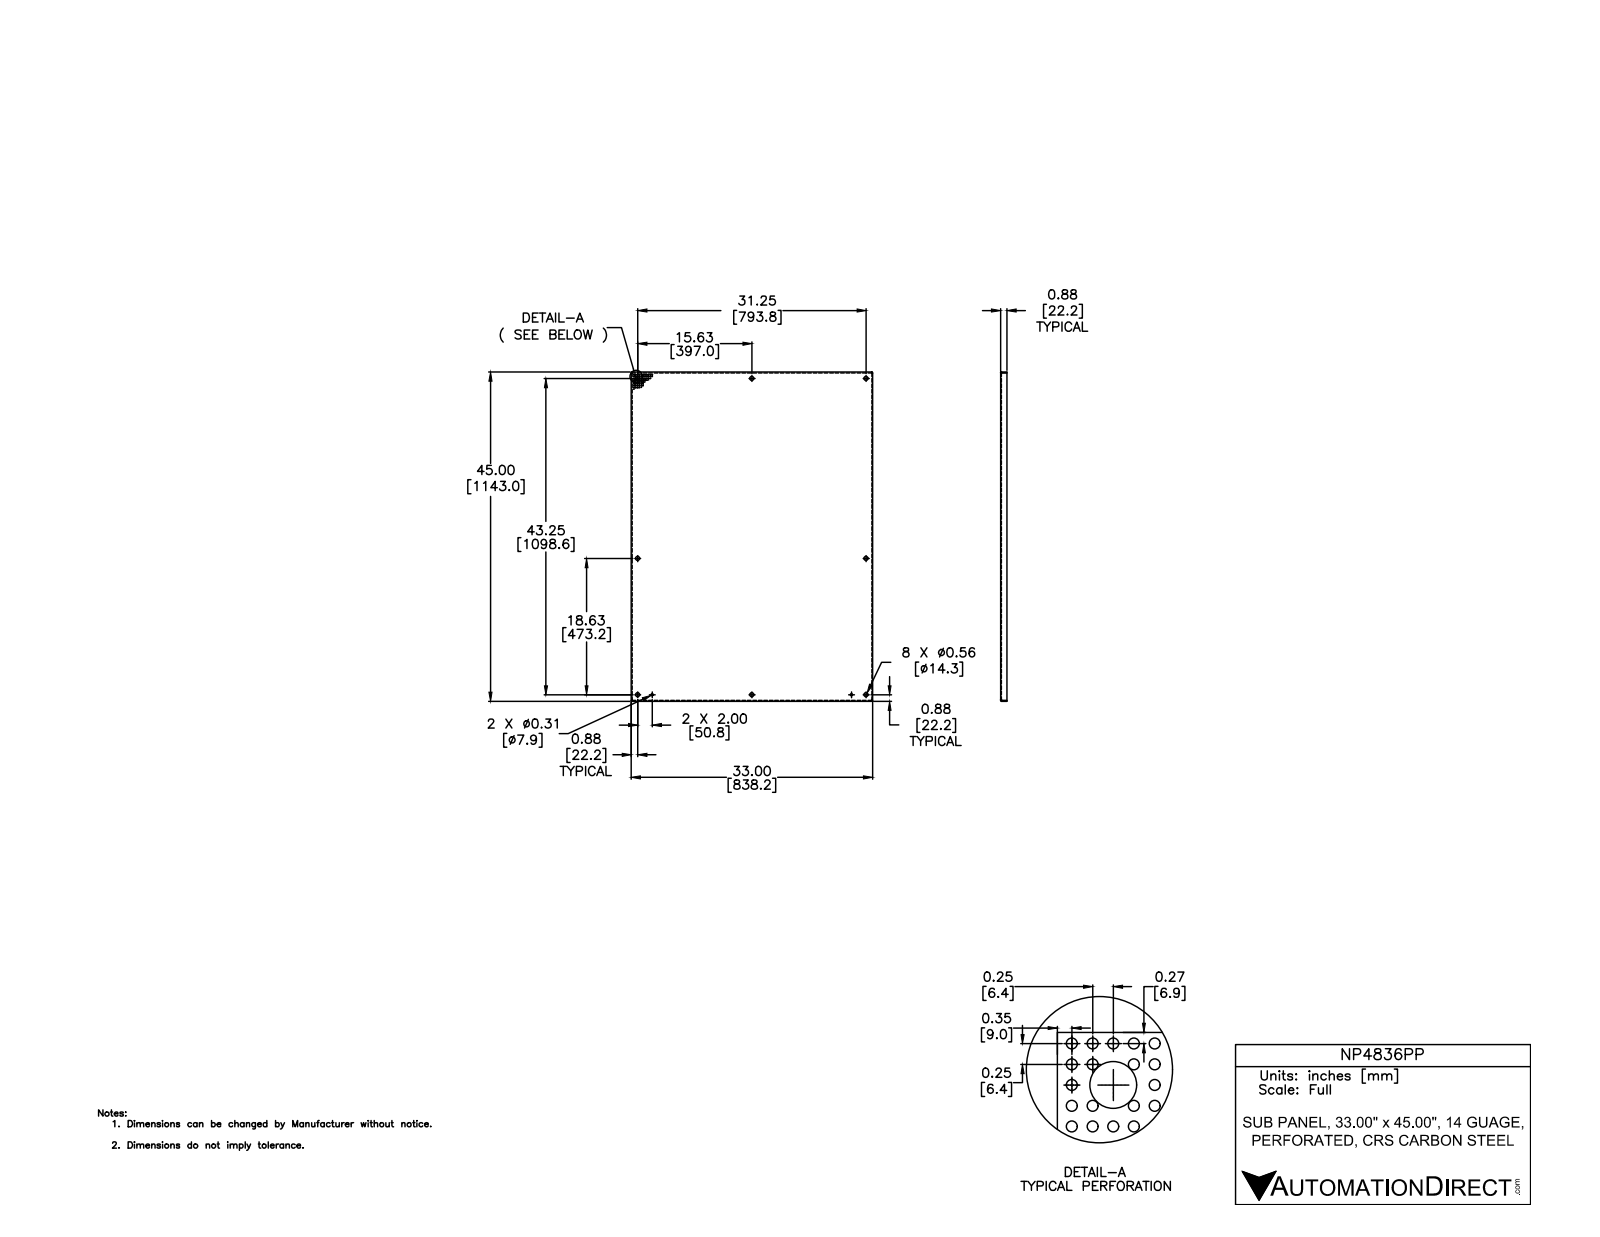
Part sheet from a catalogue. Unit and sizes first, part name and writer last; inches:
Units: inches
Overall size (bounding box): 45 × 33 × 0.875
Round holes (diameter × count): ⌀0.563 ×8, ⌀0.312 ×2
Partial cylindrical surfaces — rounded edges, fillets, slot ends (radius × count): R0.031 ×4, R0.105 ×4
Main face-to-face distances: 0.074, 32.926, 44.926, 33, 32.852, 44.852, 45, 0.801, 0.875, 0.126
Hole centre spacings: 26.679, 38.003, 31.25, 13.625, 15.625, 15.625, 21.625, 21.625
Volume: 118.6 in³ · Surface area: 3 218 in²
Bodies: 1 solid, 48 faces (22 planar, 18 cylindrical, 8 other)
Part name (STEP PRODUCT): NP_PP
STEP written by: Autodesk Inventor 2014 (AUTOMOTIVE_DESIGN)
